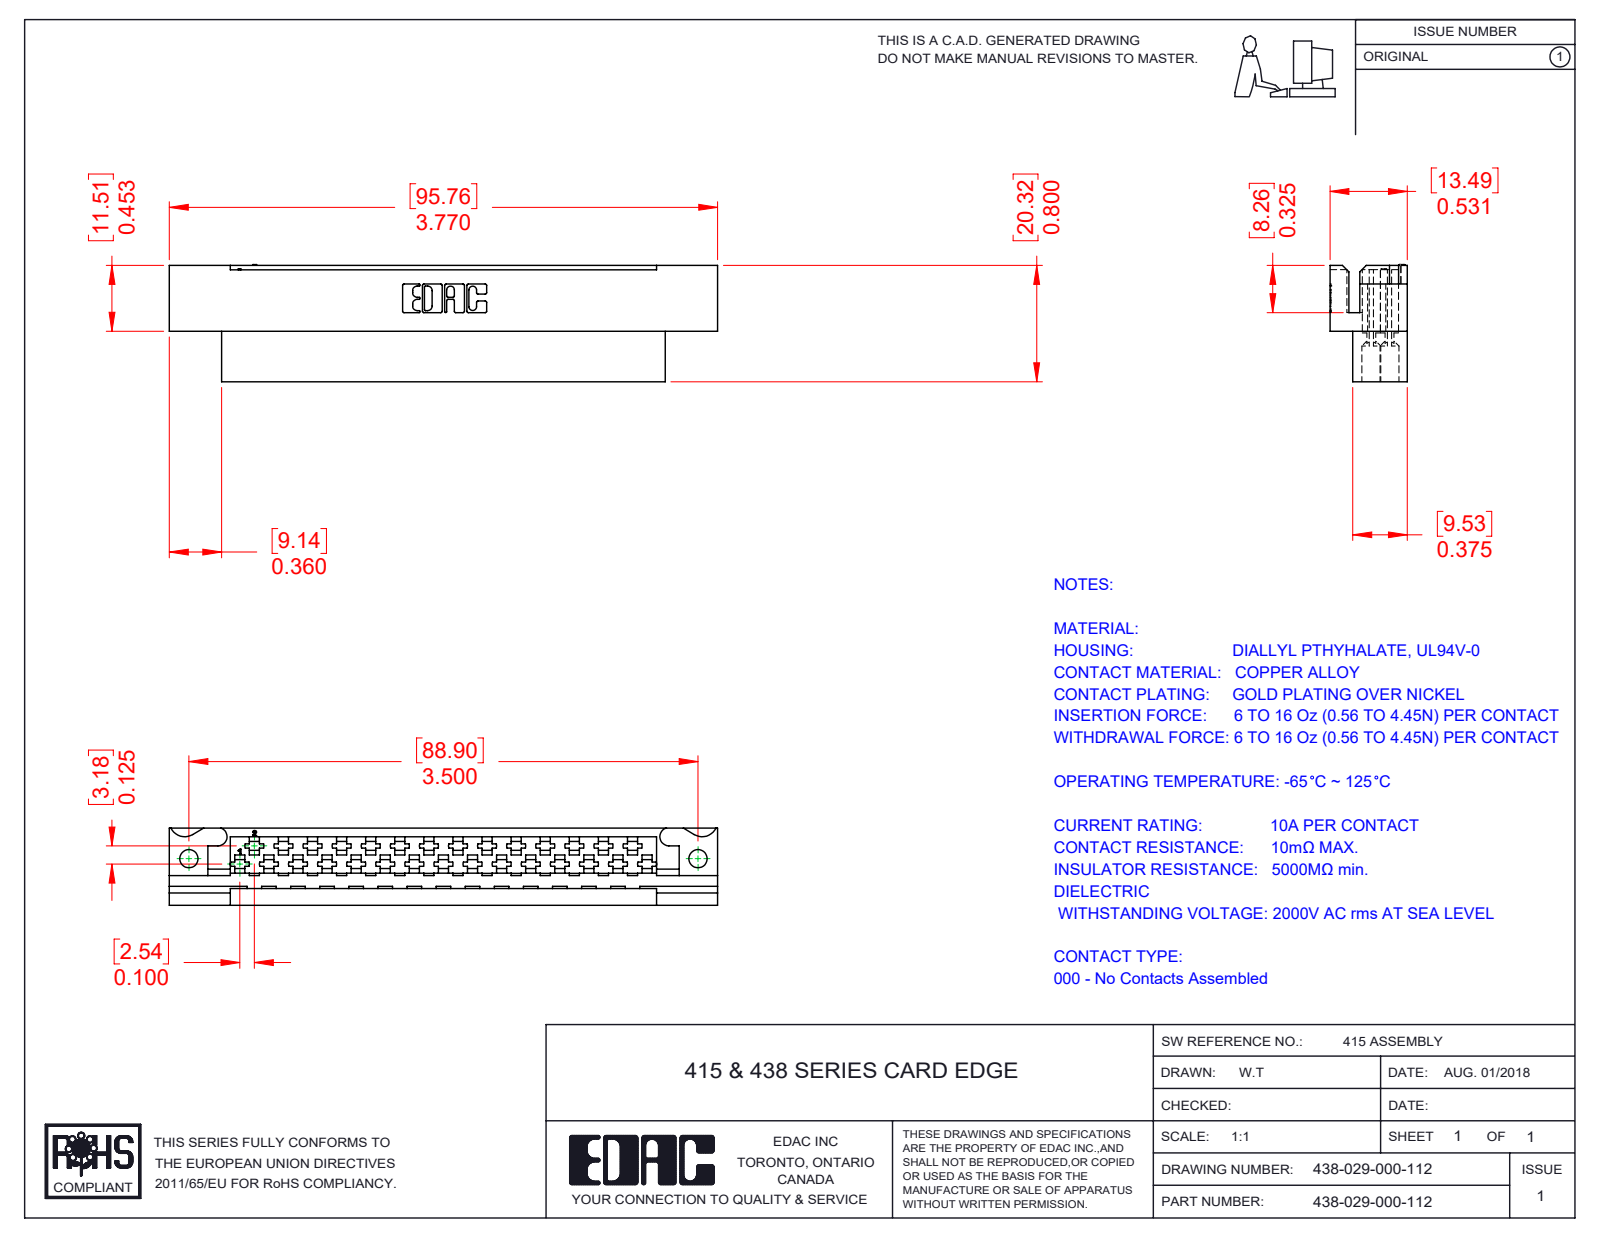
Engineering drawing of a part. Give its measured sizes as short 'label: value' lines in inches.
name: 438-210-001_438-210-029-112; 438-029-000-112
written by: SolidWorks 2016 (CONFIG_CONTROL_DESIGN)
unit: in
bodies: 1 solid, 910 faces (693 planar, 108 cylindrical, 109 other)
size: 3.77 × 0.805 × 0.531
volume: 0.886 in³; area: 22.11 in²
holes: 29× ⌀0.13, 1× ⌀0.125, 1× ⌀0.125
rounds: 22× R0.01, 6× R0.007, 6× R0.031, 3× R0.026, 2× R0.063, 2× R0.106
face distances: 0.531, 0.375, 0.156, 0.125, 0.048, 0.125, 0.172, 0.047, 0.202, 0.029
hole spacings: 0.16, 0.2, 0.325, 0.4, 0.515, 0.6, 0.711, 0.8
